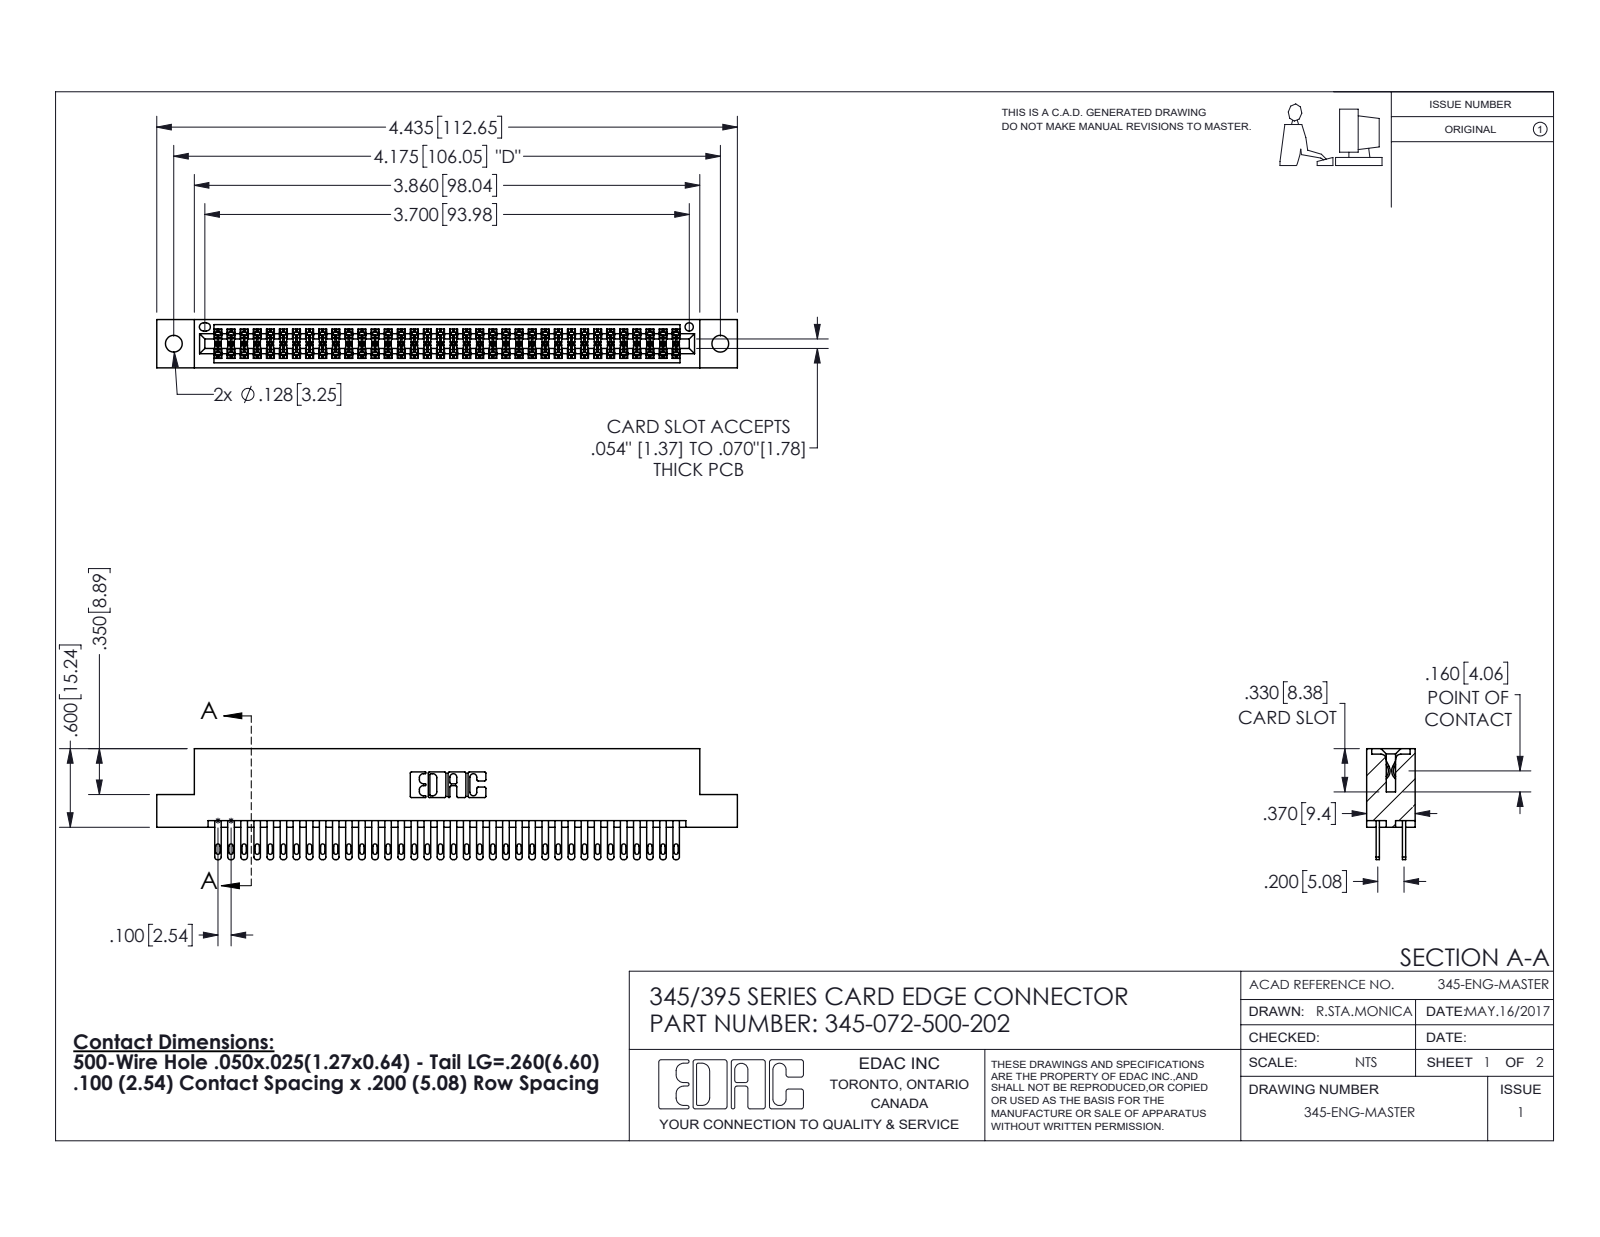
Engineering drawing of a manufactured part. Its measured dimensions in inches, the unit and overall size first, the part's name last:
Units: inches
Overall size (bounding box): 4.435 × 0.847 × 0.37
Round holes (diameter × count): ⌀0.128 ×2, ⌀0.064 ×1
Partial cylindrical surfaces — rounded edges, fillets, slot ends (radius × count): R0.006 ×108, R0.016 ×72, R0.02 ×72, R0.01 ×22, R0.007 ×6, R0.031 ×6, R0.026 ×3, R0.014 ×2
Main face-to-face distances: 0.298, 0.072, 0.2, 0.098, 0.272, 0.025, 0.37, 0.225, 0.175, 0.149
Hole centre spacings: 0.27, 3.939, 4.175
Volume: 0.676 in³ · Surface area: 25.9 in²
Bodies: 73 solids, 3438 faces (2024 planar, 1414 cylindrical, 0 other)
Part name (STEP PRODUCT): 345-072-500-202; 345-292-001_345-293-100; 345 Part_Flush Mounting Lugs - 0.128 Dia
STEP written by: SolidWorks 2016 (CONFIG_CONTROL_DESIGN)
